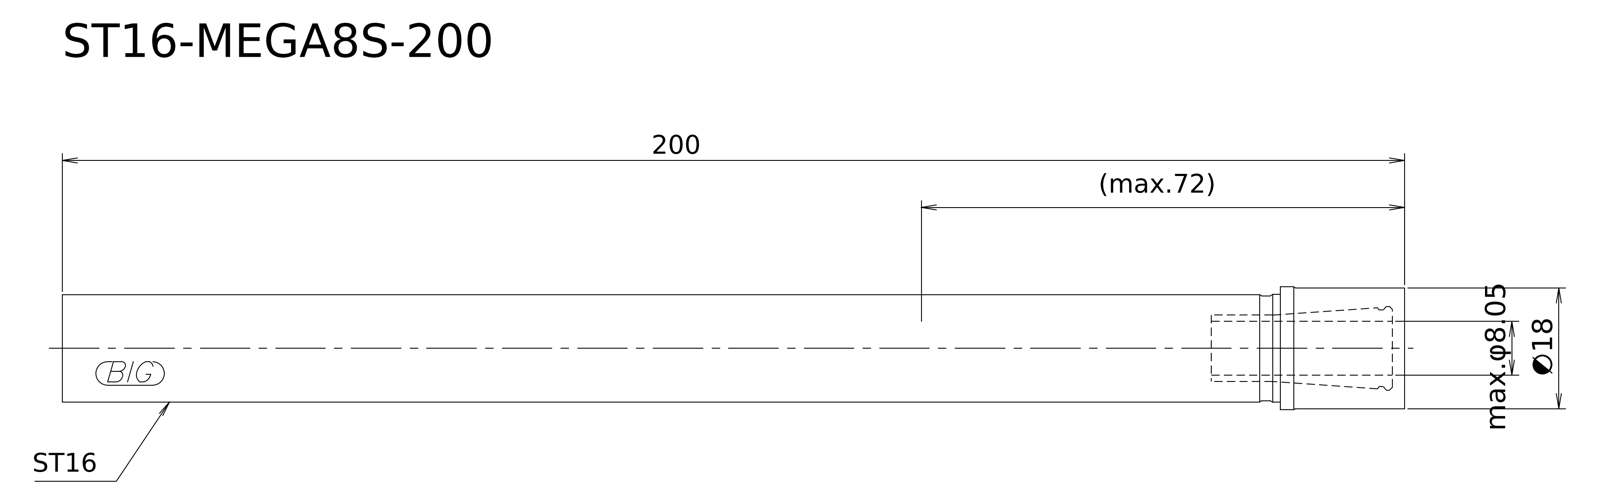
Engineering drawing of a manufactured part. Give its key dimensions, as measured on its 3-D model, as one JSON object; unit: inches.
{"step_written_by": "Kubotek KeyCreator 2011 V10.0.2 (22737) (automotive_design)", "units": "inches", "bodies": {"solids": 1, "faces": 7, "planar": 3, "cylindrical": 3, "other": 1}, "overall_size": [7.874, 0.72, 0.72], "volume_in3": 2.516, "surface_area_in2": 16.57, "round_bosses_or_shafts": [[0.72, 1], [0.709, 1], [0.63, 1]], "face_to_face_distances": [7.874, 0.728, 7.146]}
